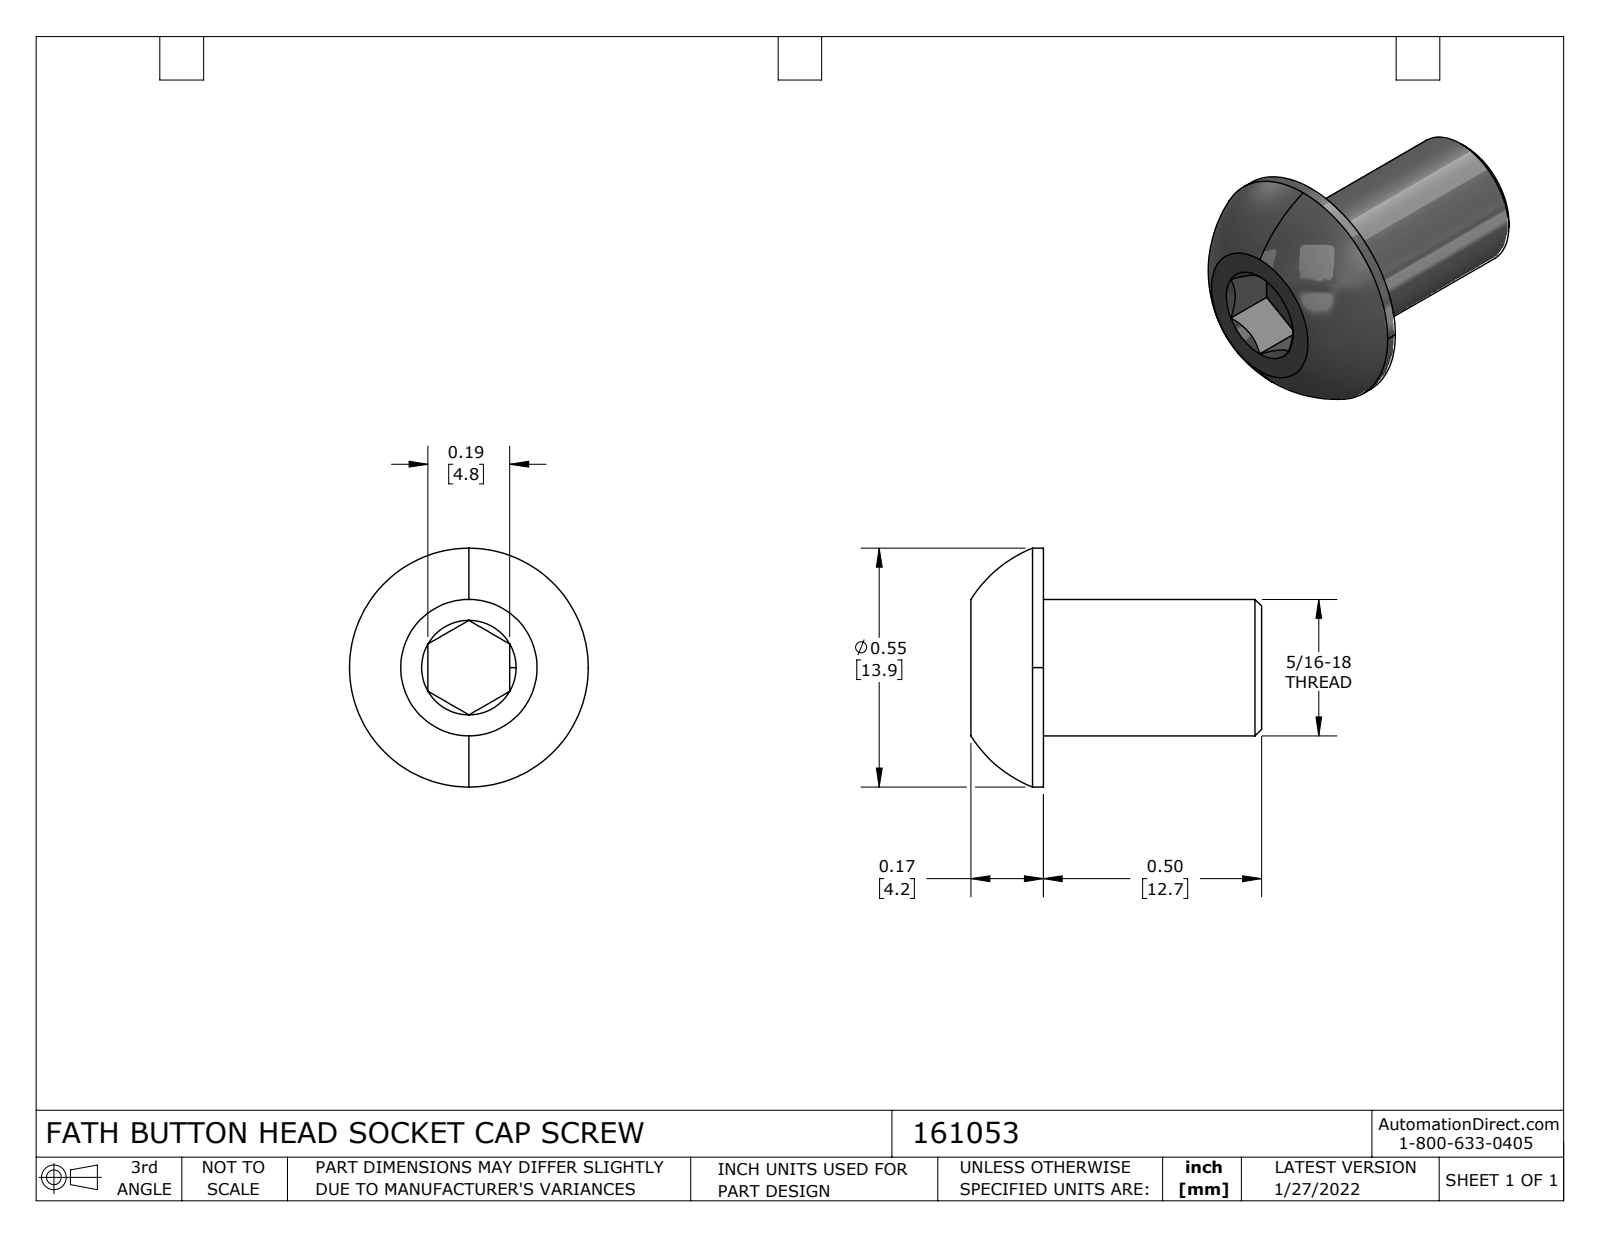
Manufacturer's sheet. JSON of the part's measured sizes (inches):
{"part_name": "161053", "step_written_by": "SolidWorks 2021 (CONFIG_CONTROL_DESIGN)", "units": "inches", "bodies": {"solids": 1, "faces": 29, "planar": 12, "cylindrical": 4, "other": 13}, "overall_size": [0.666, 0.547, 0.547], "volume_in3": 0.064, "surface_area_in2": 1.171, "round_bosses_or_shafts": [[0.547, 1], [0.313, 1]], "face_to_face_distances": [0.5, 0.666, 0.166, 0.187, 0.55, 0.05, 0.116, 0.094]}
